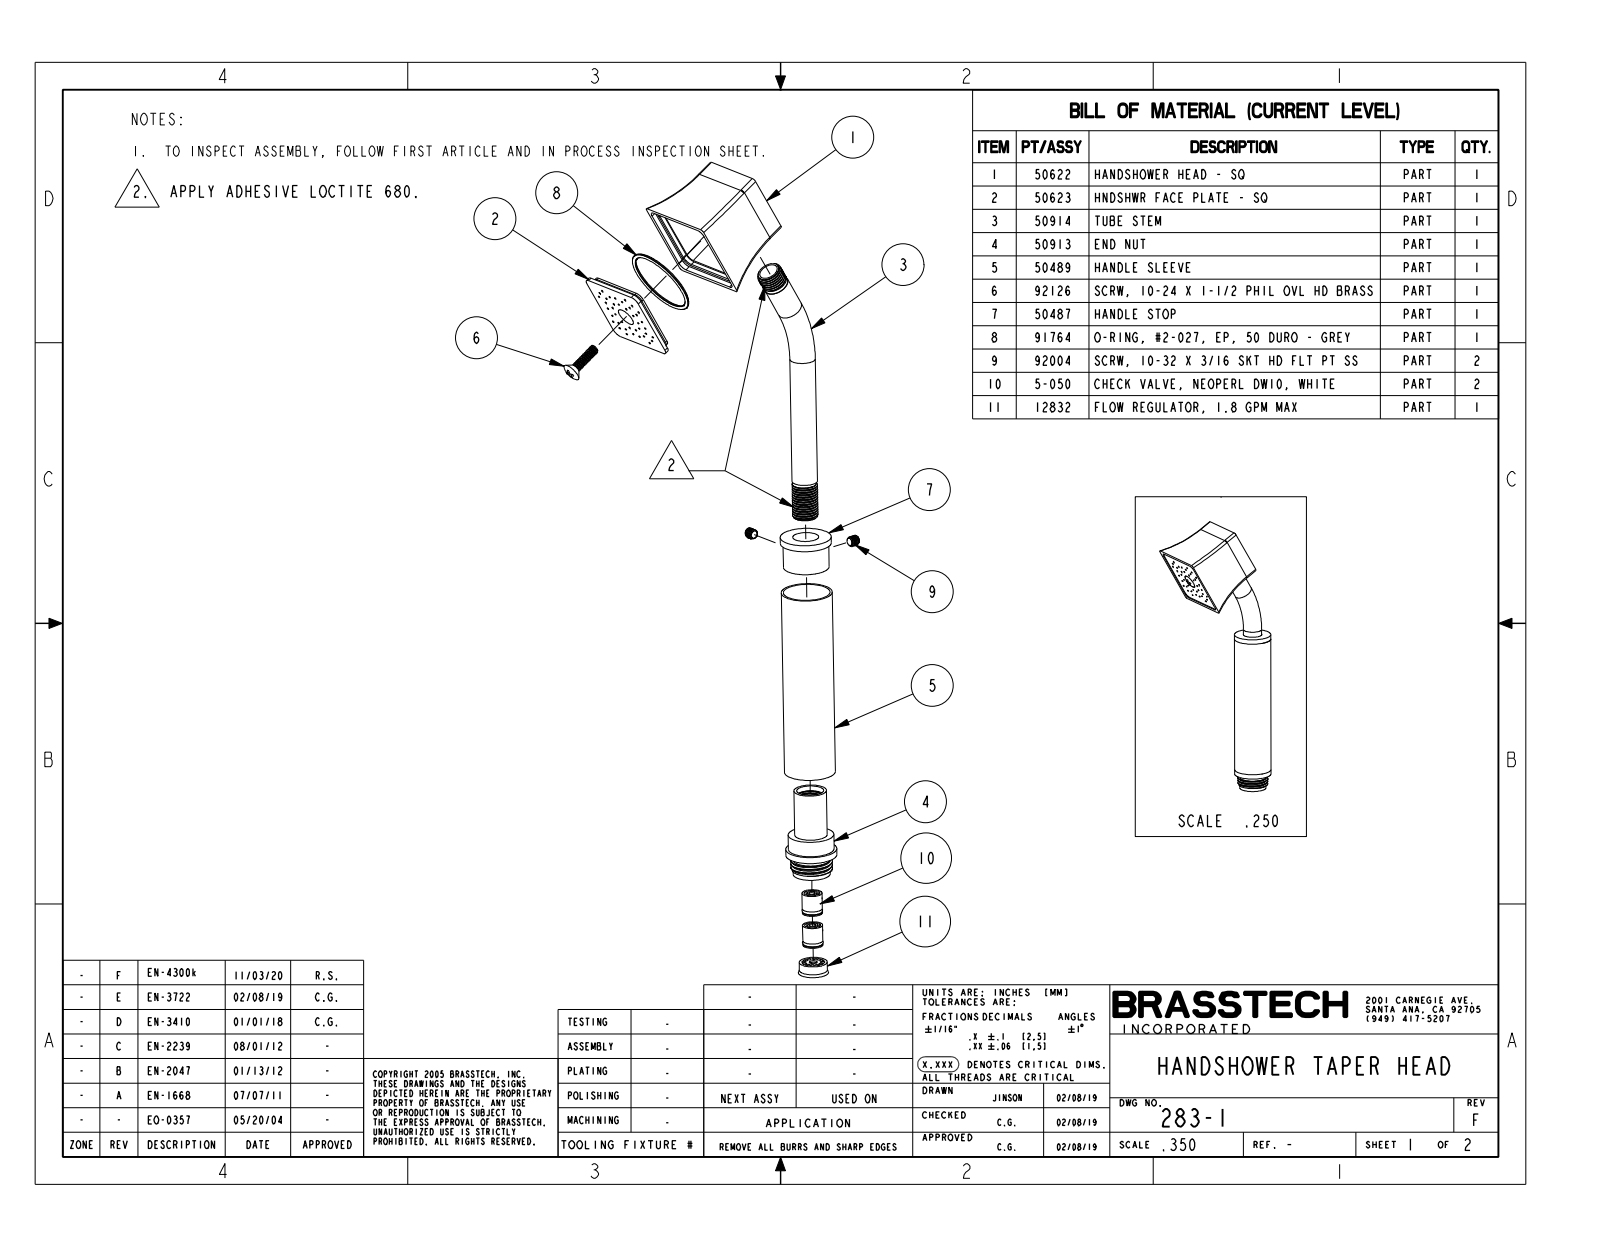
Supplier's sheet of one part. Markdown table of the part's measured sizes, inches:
| quantity | value |
| --- | --- |
| part name | 50622 |
| STEP written by | CREO PARAMETRIC BY PTC INC, 2018400 (CONFIG_CONTROL_DESIGN) |
| units | inches |
| bodies | 1 solid, 177 faces (40 planar, 117 cylindrical, 20 other) |
| overall size | 7.472 × 3.288 × 1.752 |
| volume | 7.162 in³ |
| surface area | 36.89 in² |
| round holes (diameter × count) | 0.04 × 40 |
| round bosses / shafts (diameter × count) | 0.5 × 3, 1 × 1, 0.818 × 1, 0.725 × 1 |
| partial cylindrical surfaces (radius × count) | 0.062 × 4, 0.13 × 4, 0.135 × 4, 0.19 × 4, 4.5 × 4 |
| main face-to-face distances | 1.601, 0.075, 1.526, 0.063, 0.012, 1.538, 0.019, 0.082, 0.094, 1.62 |
| hole center spacings | 0.172 |
